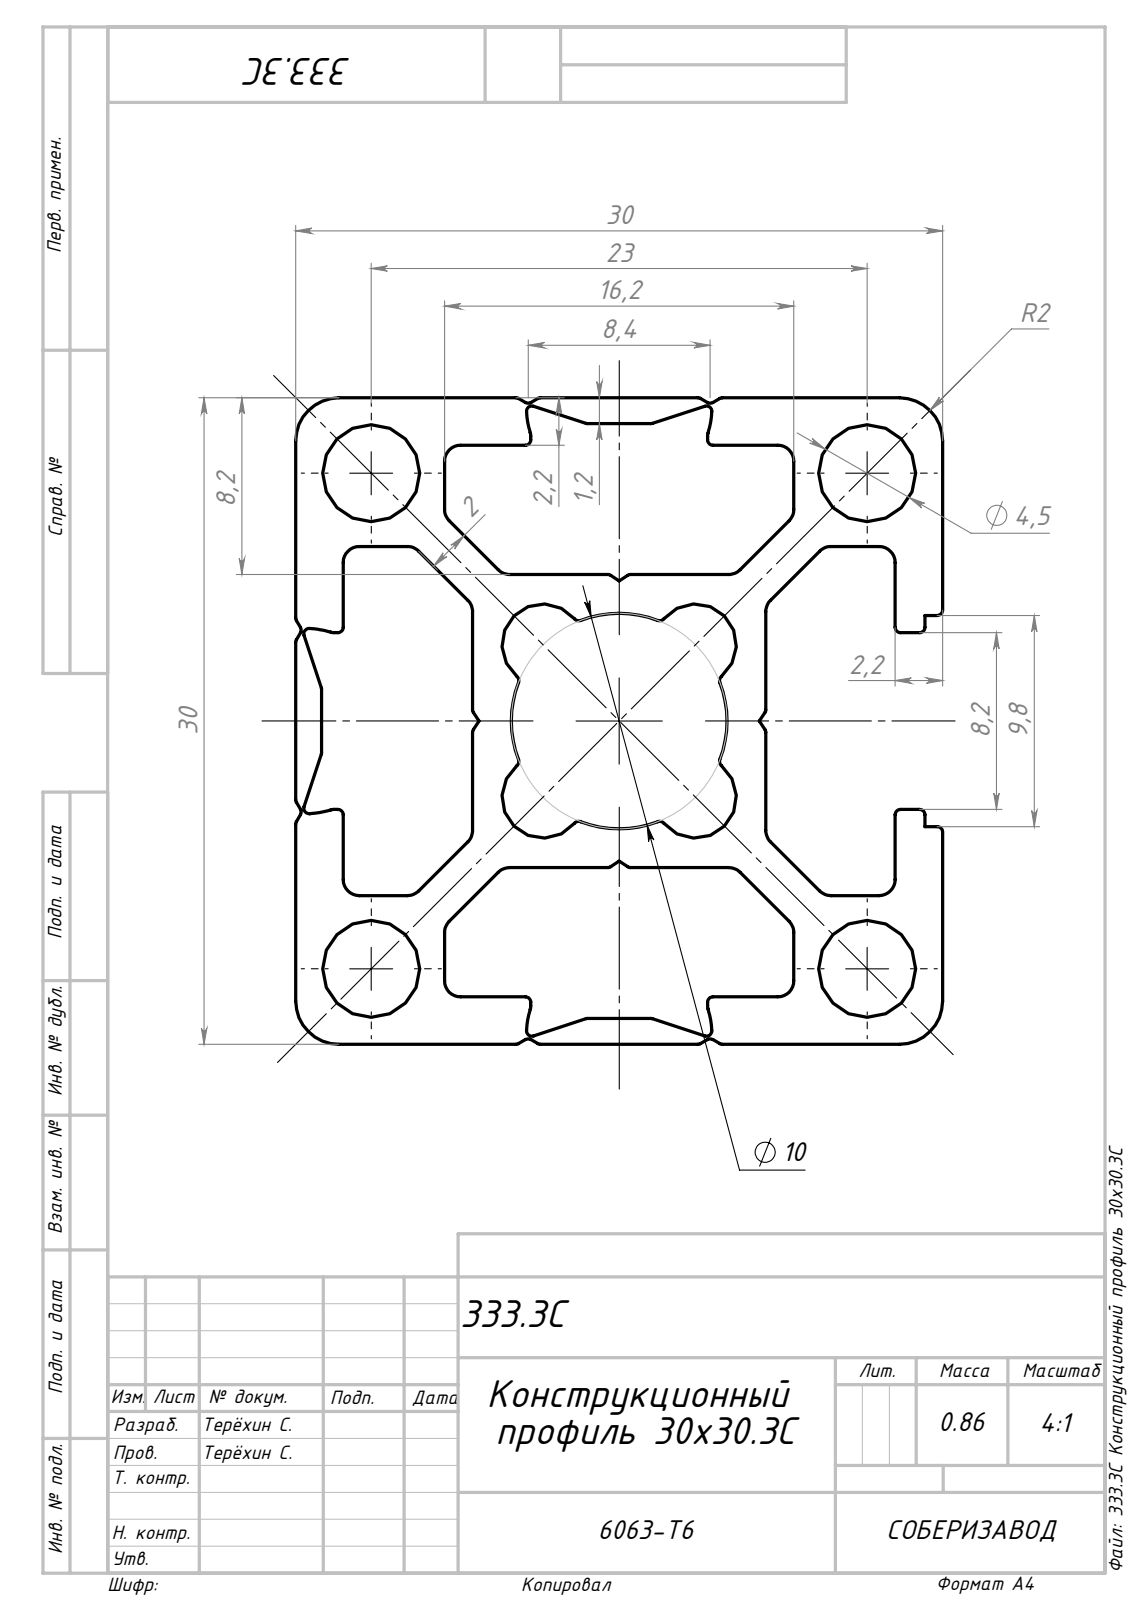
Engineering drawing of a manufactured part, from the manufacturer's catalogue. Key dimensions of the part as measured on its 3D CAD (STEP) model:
Part name (STEP PRODUCT): 333.3C Конструкционный профиль 30х30.3C
STEP written by: SolidWorks 2022 (AUTOMOTIVE_DESIGN)
Units: millimetres
Bodies: 1 solid, 209 faces (86 planar, 123 cylindrical, 0 other)
Overall size (bounding box): 1000 × 30 × 30
Volume: 318 510 mm³ · Surface area: 378 514 mm²
Round holes (diameter × count): ⌀4.5 ×4
Partial cylindrical surfaces — rounded edges, fillets, slot ends (radius × count): R0.25 ×58, R0.75 ×24, R0.6 ×6, R4.6 ×6, R1.9 ×4, R2 ×4, R5 ×1
Main face-to-face distances: 30, 8.2, 21.8, 27.8, 2.2, 6, 19.6, 13.6, 6.9, 23.1
Hole centre spacings: 23, 32.53
